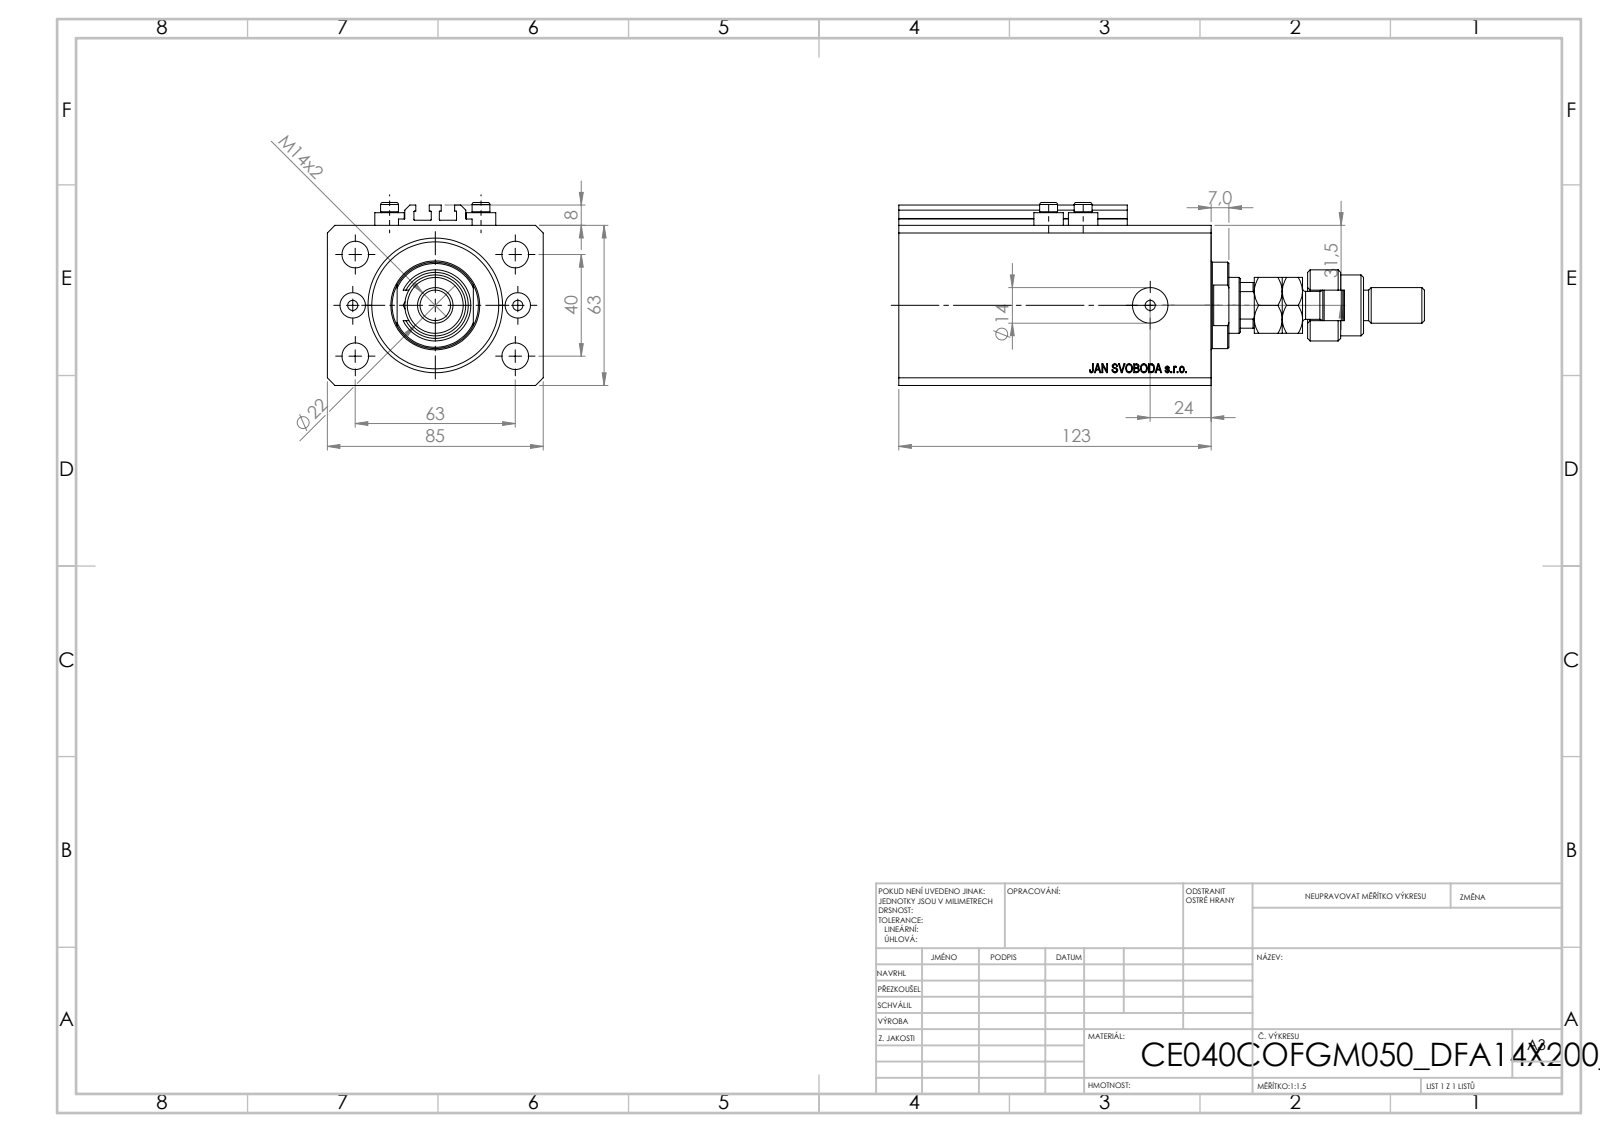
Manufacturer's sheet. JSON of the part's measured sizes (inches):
{"part_name": "ALLEN BOLT V250CE; MFA; V250CE_C_VCP; V250CE_VC_C (+2 more)", "step_written_by": "SolidWorks 2019 (CONFIG_CONTROL_DESIGN)", "units": "inches", "bodies": {"solids": 10, "faces": 1119, "planar": 532, "cylindrical": 99, "other": 488}, "overall_size": [8.15, 3.346, 2.835], "volume_in3": 37.18, "surface_area_in2": 188.6, "round_holes": [[0.157, 8], [0.413, 4], [0.394, 2], [0.551, 2], [0.492, 1], [0.866, 1], [1.575, 1], [2.087, 1]], "round_bosses_or_shafts": [[0.457, 4], [0.276, 4], [1.339, 1], [1.102, 1], [0.945, 1], [0.709, 1], [0.551, 1], [0.472, 1]], "partial_cylinders_radius": [[0.008, 10], [0.384, 1], [0.413, 1]], "face_to_face_distances": [2.48, 3.346, 4.843, 0.669, 4.173, 0.449, 3.724, 4.394, 0.394, 0.079], "hole_center_spacings": [0.788, 1.469, 2.64, 0.535, 1.28, 1.417, 1.515, 1.575]}
